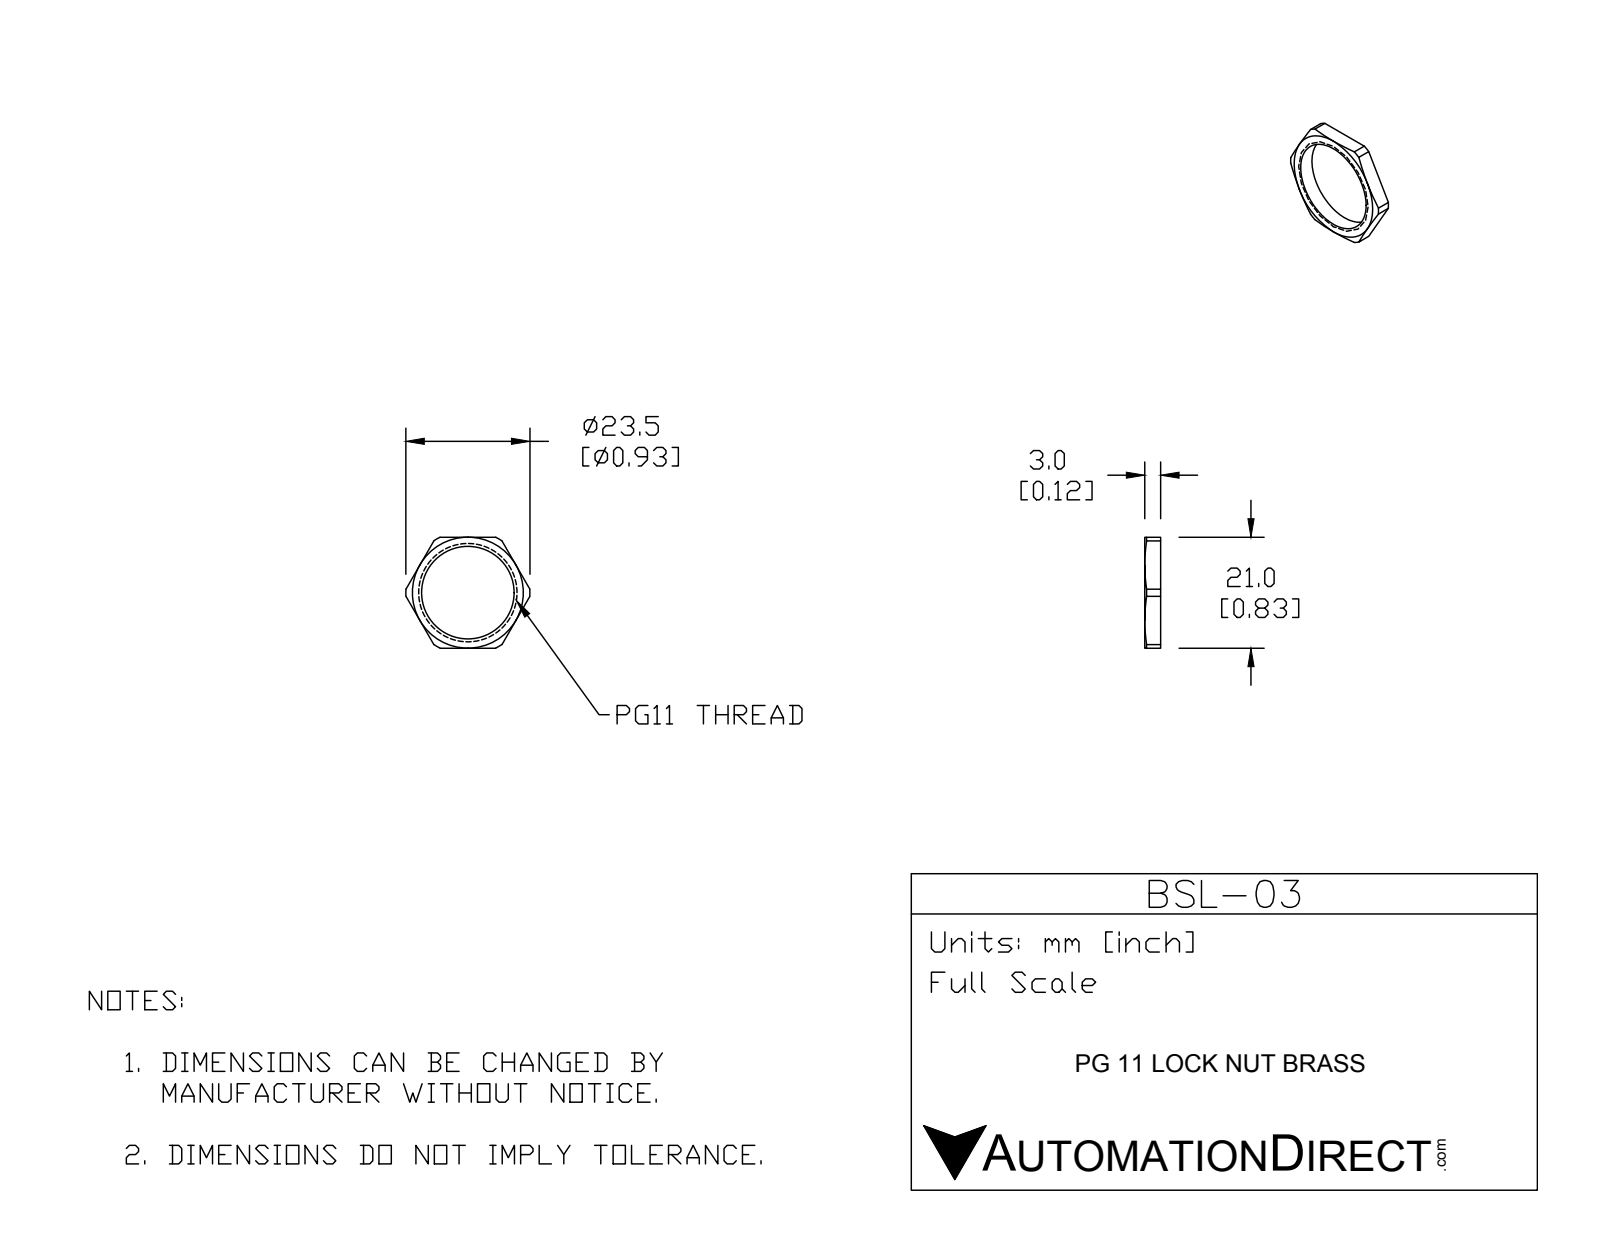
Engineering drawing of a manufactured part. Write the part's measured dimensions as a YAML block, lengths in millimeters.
part_name: "BSL-03"
step_written_by: "SolidWorks 2015 (CONFIG_CONTROL_DESIGN)"
units: millimeters
bodies: {solids: 1, faces: 23, planar: 8, cylindrical: 9, other: 6}
overall_size: [23.5, 21, 3]
volume: 415
surface_area: 650
round_holes:
  - {diameter: 17.5, count: 1}
partial_cylinders:
  - {radius: 11.75, count: 1}
face_to_face_distances: [3, 21]
